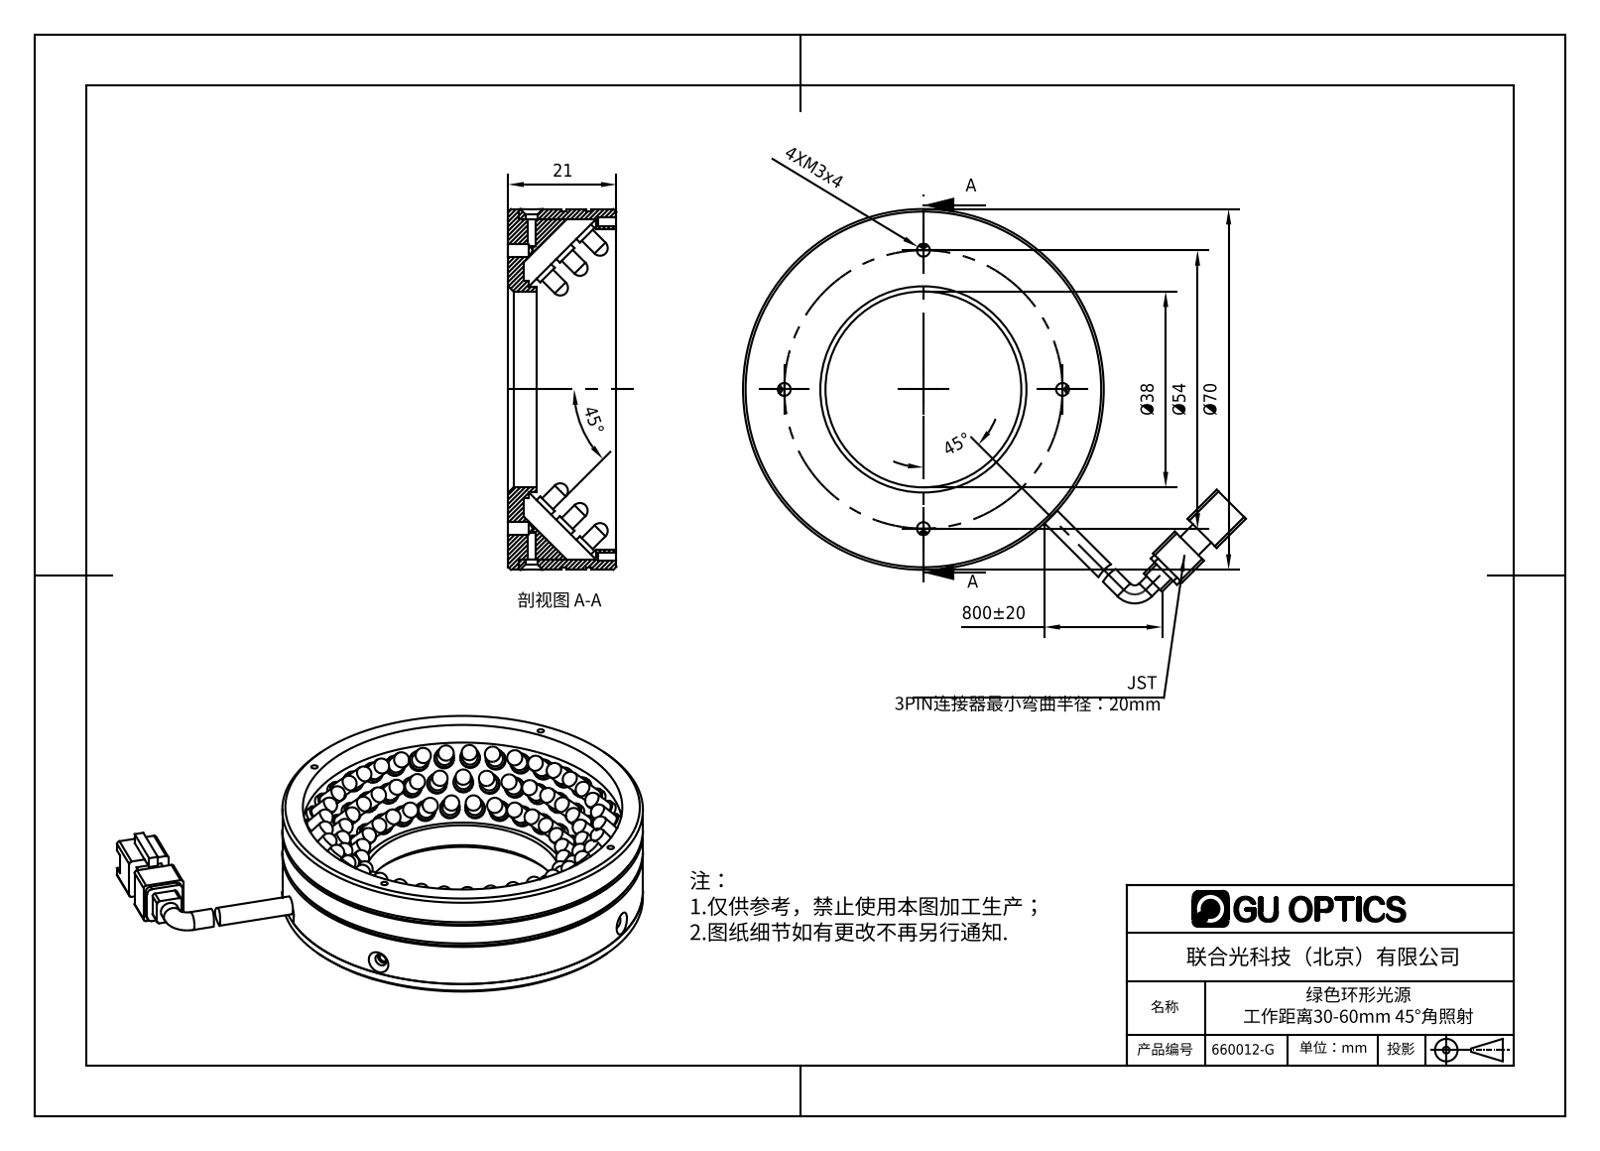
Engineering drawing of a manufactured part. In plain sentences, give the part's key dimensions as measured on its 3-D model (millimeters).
The part is named "660012-G". Its 3-D file was written by "SolidWorks 2016 (AUTOMOTIVE_DESIGN)". It is 103 solids with 1900 faces: 1251 planar, 494 cylindrical and 155 other. Overall it measures 97.58 by 76.52 by 21 millimeters. Its volume is 29 732 cubic millimeters and its surface area 35 149 square millimeters. Round holes: 4 of diameter 1.25, 4 of diameter 2.5, 3 of diameter 3, 2 of diameter 1.6, 2 of diameter 2.4, 1 of diameter 38, 1 of diameter 62. Round bosses or shafts: 98 of diameter 3.8, 97 of diameter 3, 2 of diameter 3.5, 1 of diameter 70, 1 of diameter 69, 1 of diameter 66, 1 of diameter 42, 1 of diameter 40. Partial cylindrical surfaces (rounded edges, fillets, slot ends): 8 of radius 0.5, 4 of radius 1, 1 of radius 1.65, 1 of radius 5. The main face-to-face distances are 1, 2, 3, 19, 4, 21, 17, 18, 0.5, 14. The hole center spacings are 42.25, 5.5, 27, 32.5, 38.18, 45.96, 59.5, 54.
